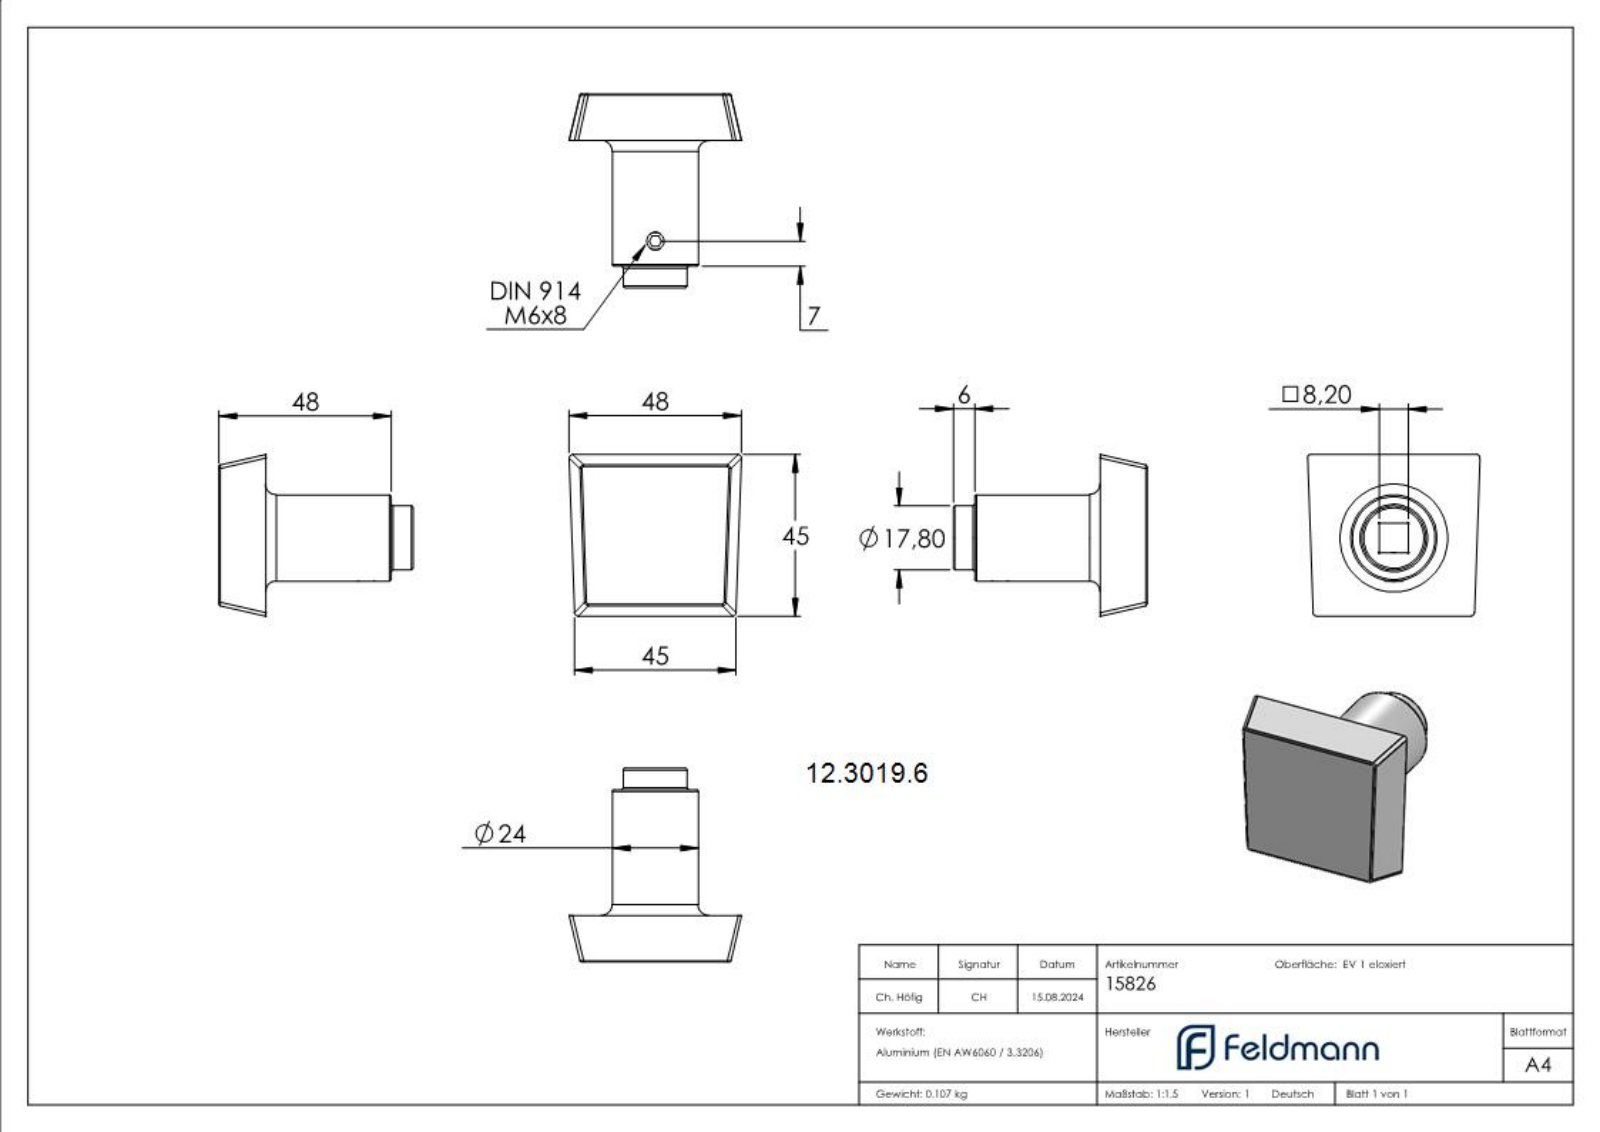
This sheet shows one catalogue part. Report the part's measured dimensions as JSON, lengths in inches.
{"part_name": "DIN914_DIN 914 M6x8; 15727 Teil1_15826 Teil1; 15826", "step_written_by": "SolidWorks 2018 (CONFIG_CONTROL_DESIGN)", "units": "inches", "bodies": {"solids": 2, "faces": 234, "planar": 116, "cylindrical": 20, "other": 98}, "overall_size": [2.126, 1.89, 1.772], "volume_in3": 2.364, "surface_area_in2": 16.05, "round_holes": [[0.197, 1]], "round_bosses_or_shafts": [[0.945, 1], [0.701, 1], [0.236, 1]], "partial_cylinders_radius": [[0.039, 8], [0.01, 4], [0.02, 4]], "face_to_face_distances": [0.512, 0.323, 1.614, 2.126, 0.236, 1.378, 1.89, 0.157, 1.457, 1.22]}
